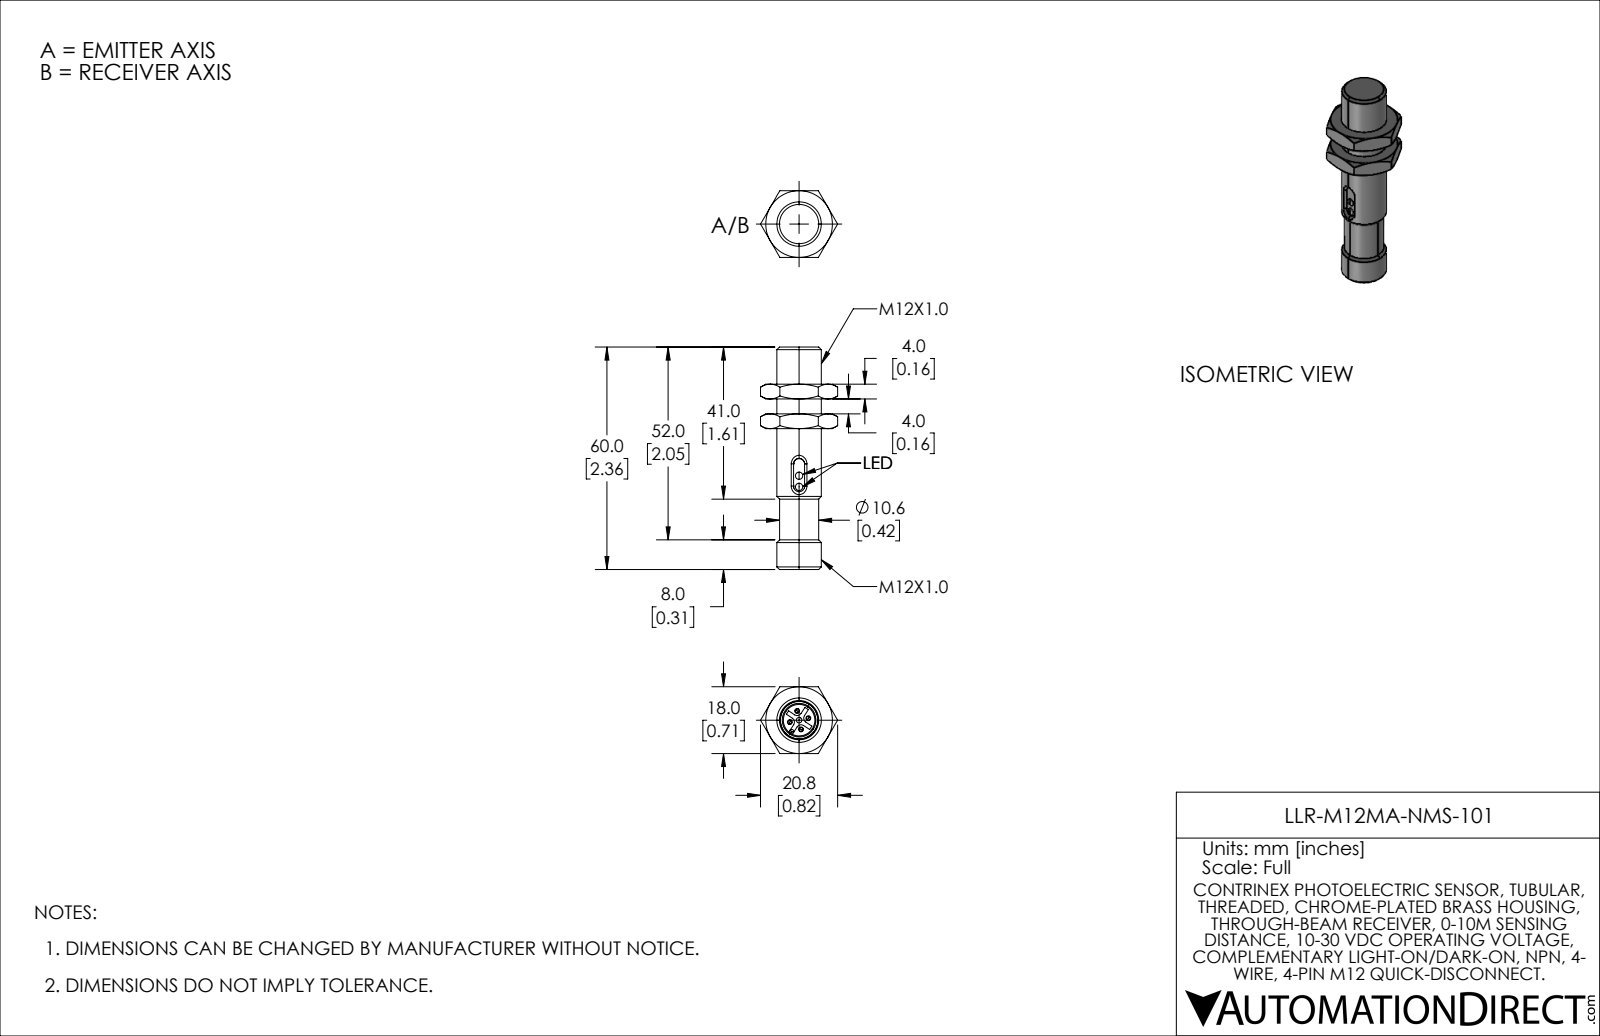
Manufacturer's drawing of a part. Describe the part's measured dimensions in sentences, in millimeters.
The part is named "LLR-M12MA-NMS-101". Its 3-D file was written by "SolidWorks 2021 (AUTOMOTIVE_DESIGN)". It is 3 solids with 169 faces: 44 planar, 54 cylindrical and 71 other. Overall it measures 60 by 20.79 by 18 millimeters. Its volume is 7 487 cubic millimeters and its surface area 4 205 square millimeters. Round holes: 1 of diameter 1.5, 1 of diameter 8.5, 1 of diameter 10.2, 1 of diameter 12. Round bosses or shafts: 4 of diameter 1, 1 of diameter 10.55. Partial cylindrical surfaces (rounded edges, fillets, slot ends): 4 of radius 1.25, 2 of radius 0.5, 2 of radius 1.5, 1 of radius 0.55. The main face-to-face distances are 4, 18, 8, 12, 14, 10, 22, 51.2, 41.2, 37.2.
